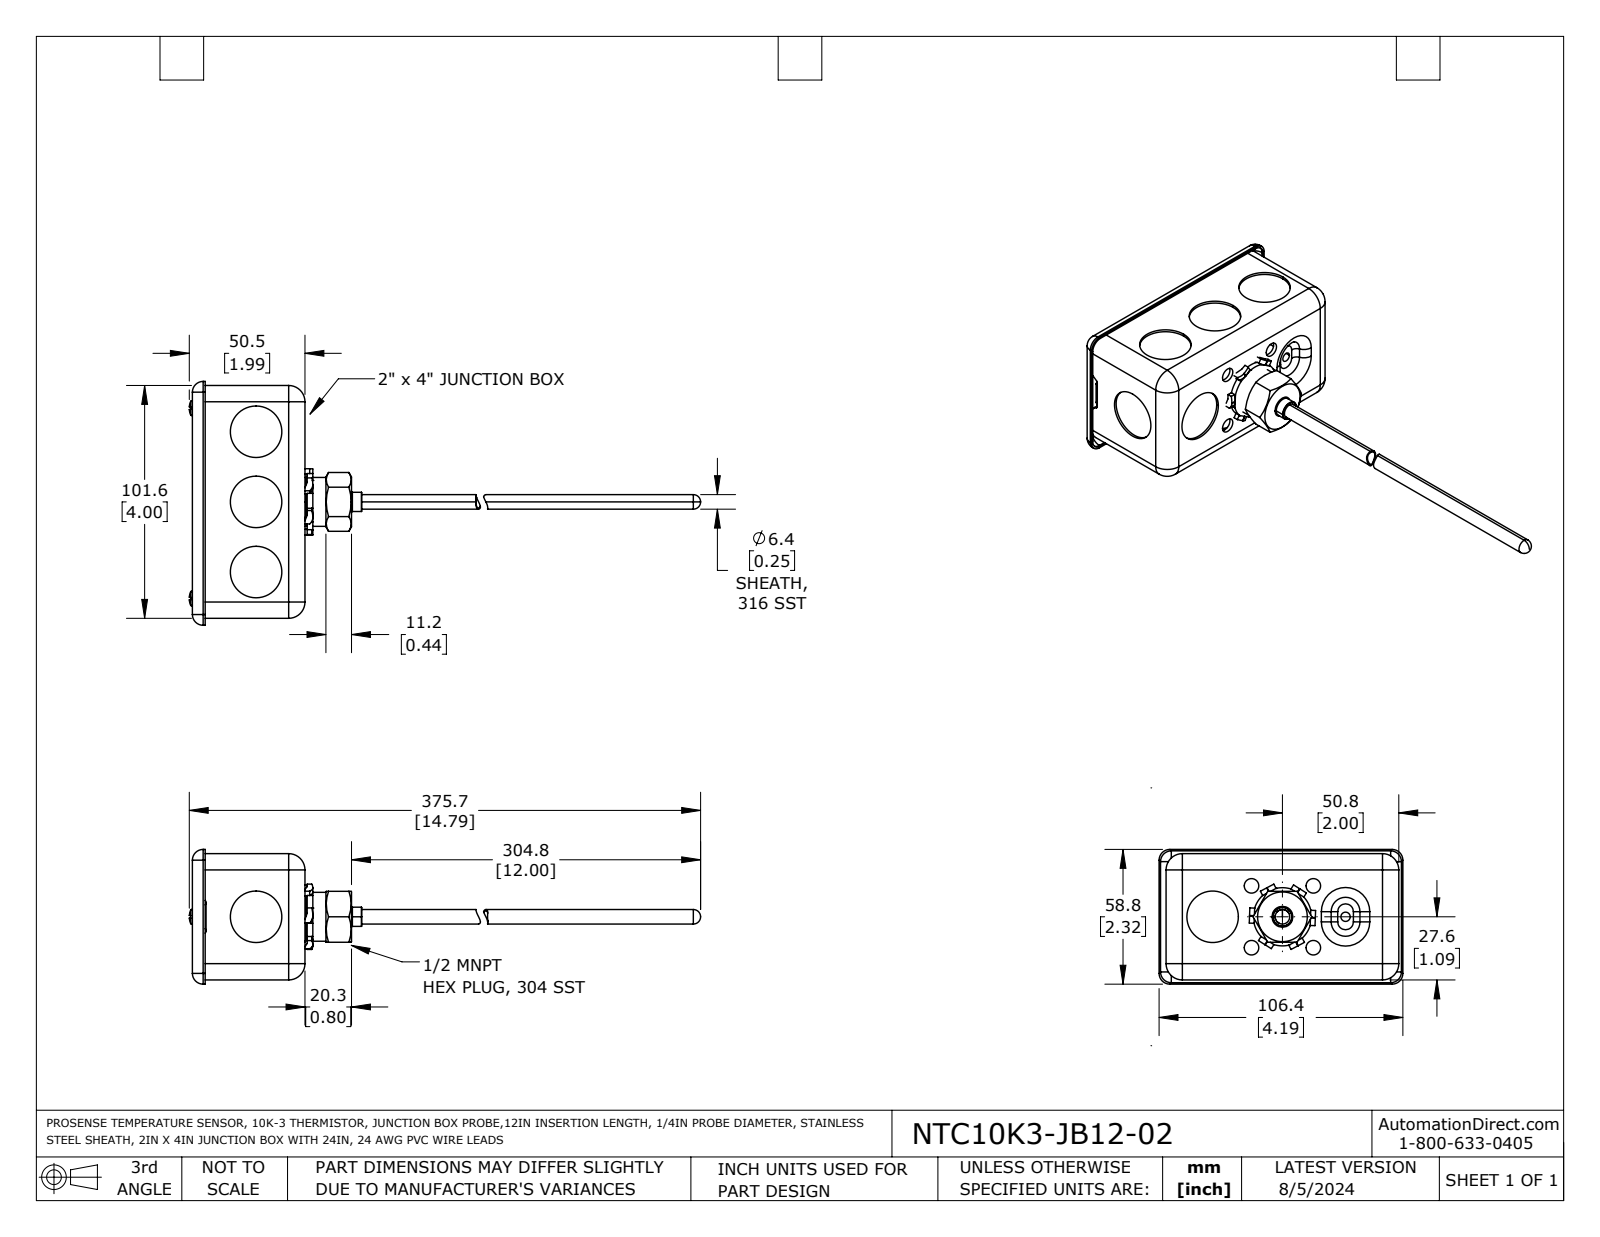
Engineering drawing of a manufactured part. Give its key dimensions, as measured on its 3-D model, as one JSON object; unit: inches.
{"part_name": "NTC10K3-JB12-02", "step_written_by": "SolidWorks 2021 (AUTOMOTIVE_DESIGN)", "units": "inches", "bodies": {"solids": 5, "faces": 358, "planar": 153, "cylindrical": 143, "other": 62}, "overall_size": [14.783, 4.19, 2.315], "volume_in3": 2.901, "surface_area_in2": 107.3, "round_holes": [[0.885, 6], [0.25, 4], [0.115, 2], [0.16, 1], [0.21, 1], [0.253, 1], [0.438, 1]], "round_bosses_or_shafts": [[0.136, 2], [0.84, 1], [0.33, 1], [0.25, 1]], "partial_cylinders_radius": [[0.185, 16], [0.245, 8], [0.28, 8], [0.174, 6], [0.555, 6], [0.045, 4], [0.165, 4], [0.07, 2]], "face_to_face_distances": [0.07, 0.03, 2.03, 2.1, 0.04, 0.1, 0.06, 1.855, 2.07, 2.13], "hole_center_spacings": [0.751, 1.062, 1.248, 2.254, 0.767, 0.854, 1.205, 1.502]}
